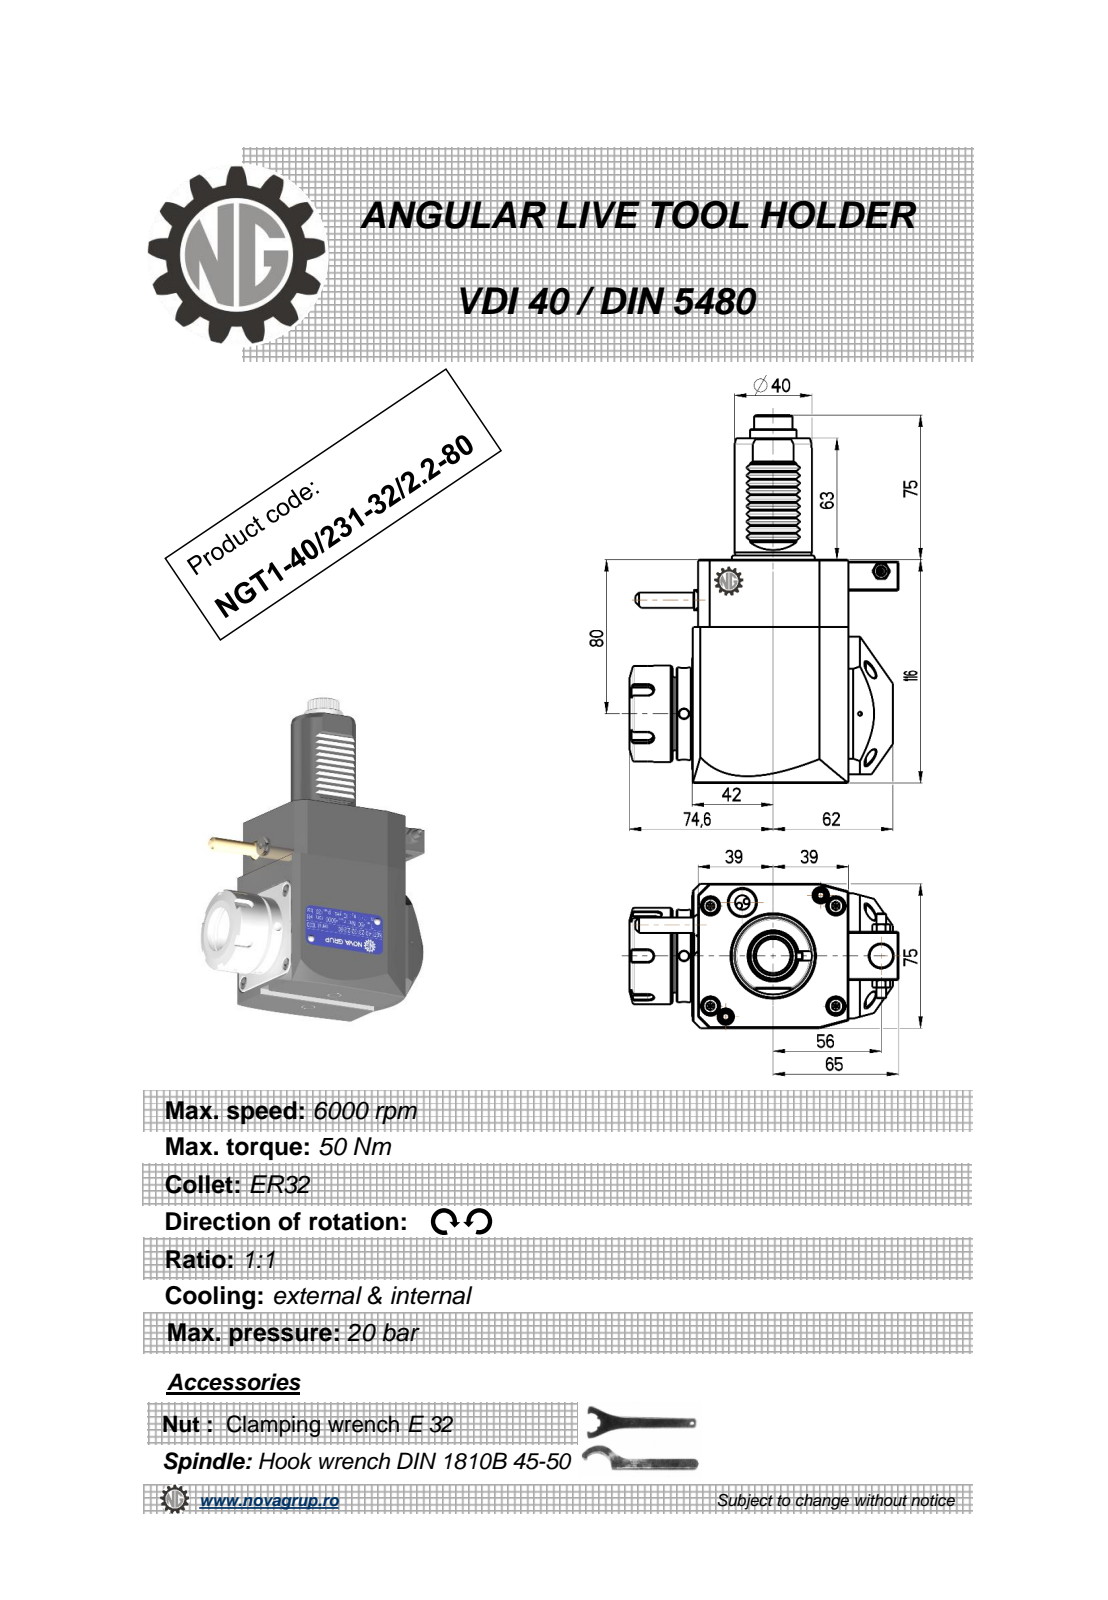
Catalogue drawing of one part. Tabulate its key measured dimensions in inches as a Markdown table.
| quantity | value |
| --- | --- |
| part name | NGT1_40_231_32_2_2_80 |
| STEP written by | PRO/ENGINEER BY PARAMETRIC TECHNOLOGY CORPORATION, 2010280 (CONFIG_CONTROL_DESIGN) |
| units | inches |
| bodies | 1 solid, 538 faces (199 planar, 185 cylindrical, 154 other) |
| overall size | 7.52 × 5.496 × 3.016 |
| volume | 54.54 in³ |
| surface area | 110.1 in² |
| round holes (diameter × count) | 0.197 × 3, 0.118 × 1, 0.165 × 1, 0.374 × 1, 0.472 × 1, 1.063 × 1 |
| round bosses / shafts (diameter × count) | 1.969 × 1, 1.89 × 1, 1.614 × 1, 1.575 × 1, 0.945 × 1, 0.441 × 1, 0.353 × 1, 0.315 × 1 |
| partial cylindrical surfaces (radius × count) | 0.082 × 48, 0.01 × 12, 0.012 × 10, 0.009 × 6, 0.118 × 5, 0.357 × 1, 0.391 × 1, 0.591 × 1 |
| main face-to-face distances | 2.953, 4.567, 3.189, 0.118, 3.071, 0.11, 3.181, 4.409, 0.177, 0.295 |
| hole center spacings | 0.799, 2.407, 2.815, 4.026, 4.969 |
